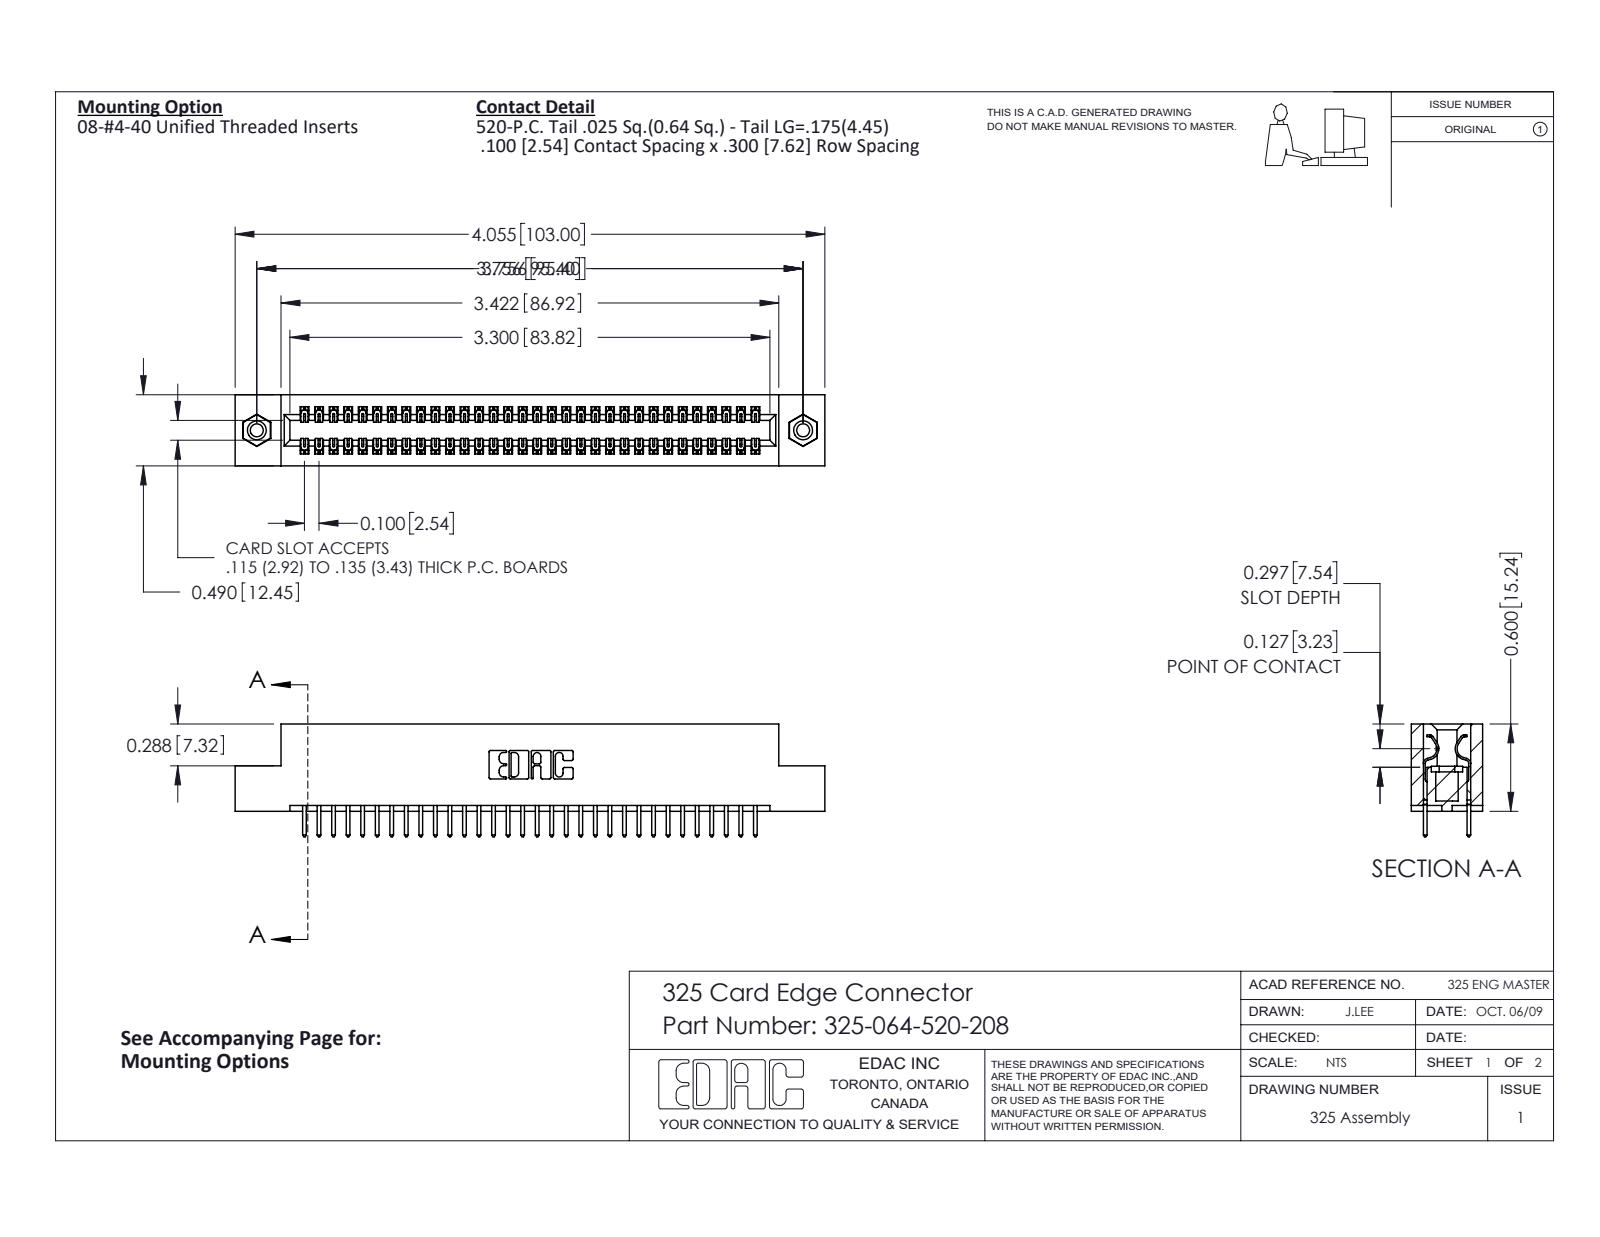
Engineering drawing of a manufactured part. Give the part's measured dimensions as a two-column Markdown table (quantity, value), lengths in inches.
| quantity | value |
| --- | --- |
| part name | 325 Part_TI; 325-292-001_325-293-120; 345-250-001_345-250-003-102; 325-064-520-208 |
| STEP written by | SolidWorks 2016 (CONFIG_CONTROL_DESIGN) |
| units | inches |
| bodies | 67 solids, 3502 faces (2406 planar, 1080 cylindrical, 16 other) |
| overall size | 4.055 × 0.775 × 0.49 |
| volume | 0.805 in³ |
| surface area | 24.2 in² |
| round holes (diameter × count) | 0.089 × 2, 0.125 × 2, 0.16 × 2 |
| round bosses / shafts (diameter × count) | 0.155 × 2 |
| partial cylindrical surfaces (radius × count) | 0.006 × 96, 0.01 × 64, 0.01 × 22, 0.007 × 6, 0.031 × 6, 0.026 × 3, 0.014 × 2, 0.022 × 2 |
| main face-to-face distances | 0.083, 0.407, 0.3, 0.49, 0.107, 0.383, 0.025, 0.325, 0.275, 0.04 |
| hole center spacings | 3.756 |
